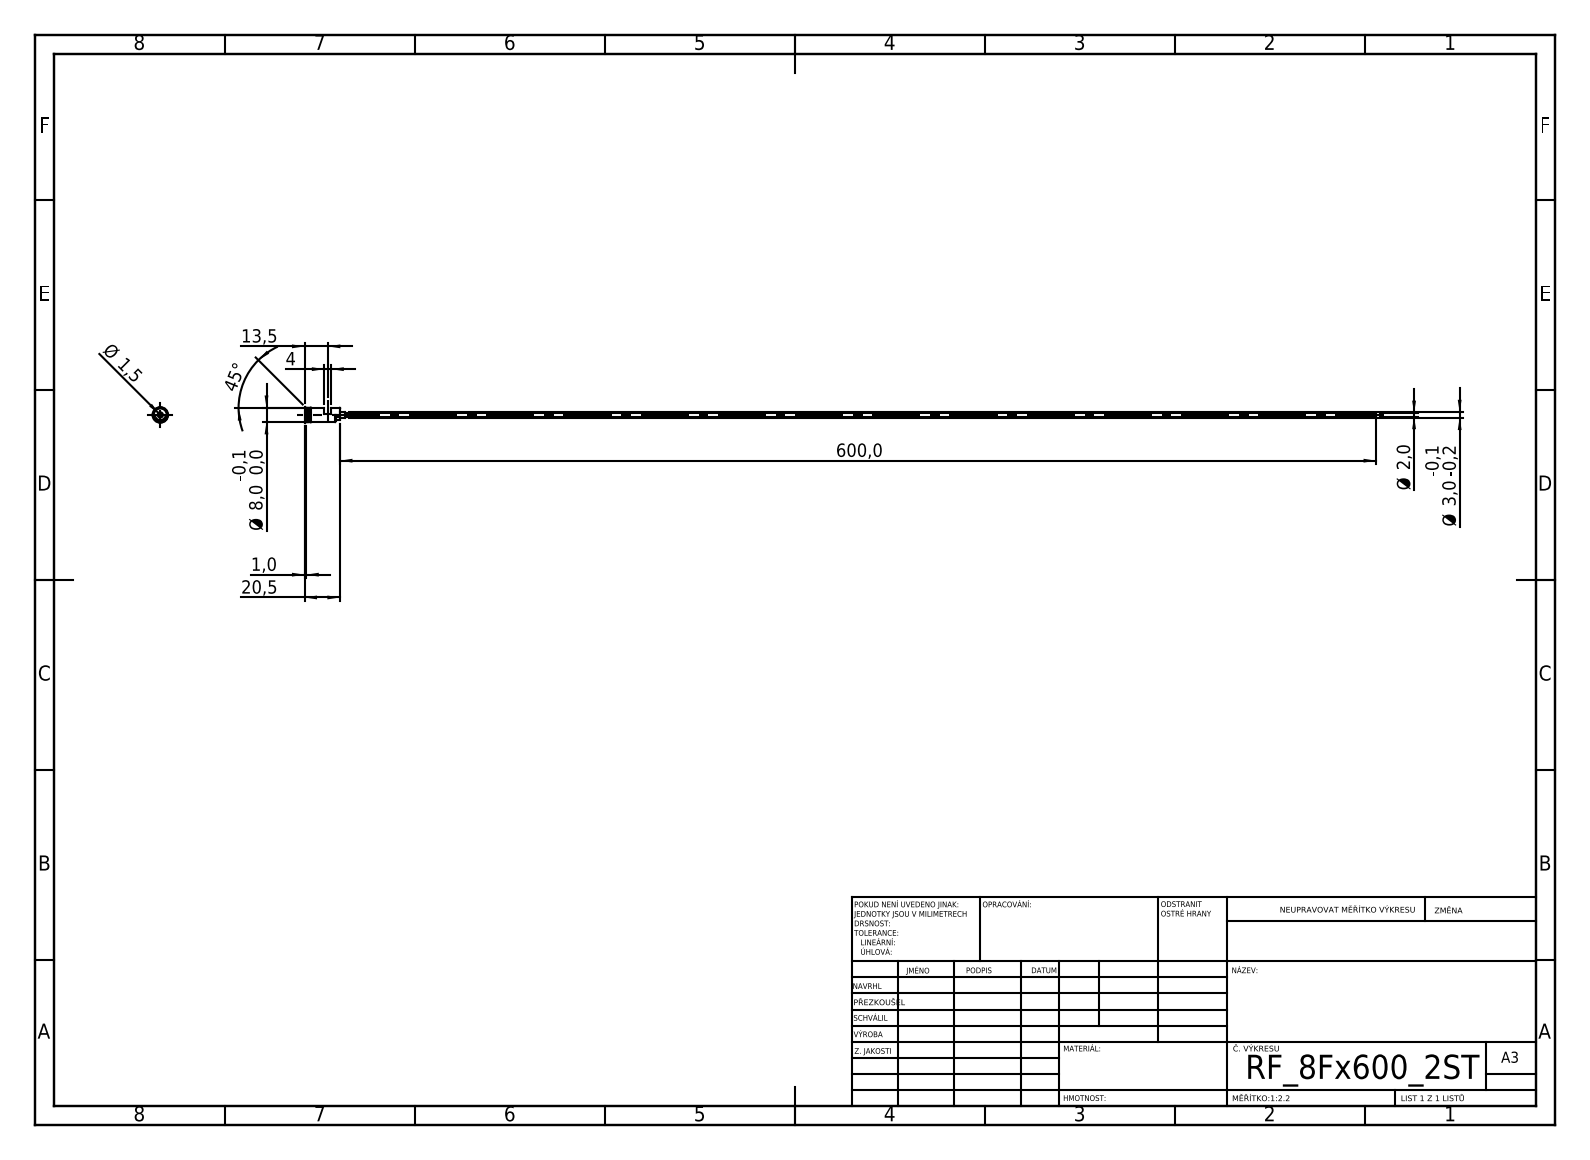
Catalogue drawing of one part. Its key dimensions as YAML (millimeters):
step_written_by: "SolidWorks 2019 (CONFIG_CONTROL_DESIGN)"
units: millimeters
bodies: {solids: 1, faces: 55, planar: 24, cylindrical: 19, other: 12}
overall_size: [620.5, 9, 9]
volume: 1730
surface_area: 7338
round_holes:
  - {diameter: 1.5, count: 1}
round_bosses_or_shafts:
  - {diameter: 9, count: 1}
  - {diameter: 8, count: 1}
  - {diameter: 7.8, count: 1}
  - {diameter: 3, count: 1}
  - {diameter: 2, count: 1}
partial_cylinders:
  - {radius: 3, count: 2}
  - {radius: 3.05, count: 1}
face_to_face_distances: [4, 20.5, 9, 11.5, 5, 15.5, 2.5, 18.5, 13.5, 9.5]
